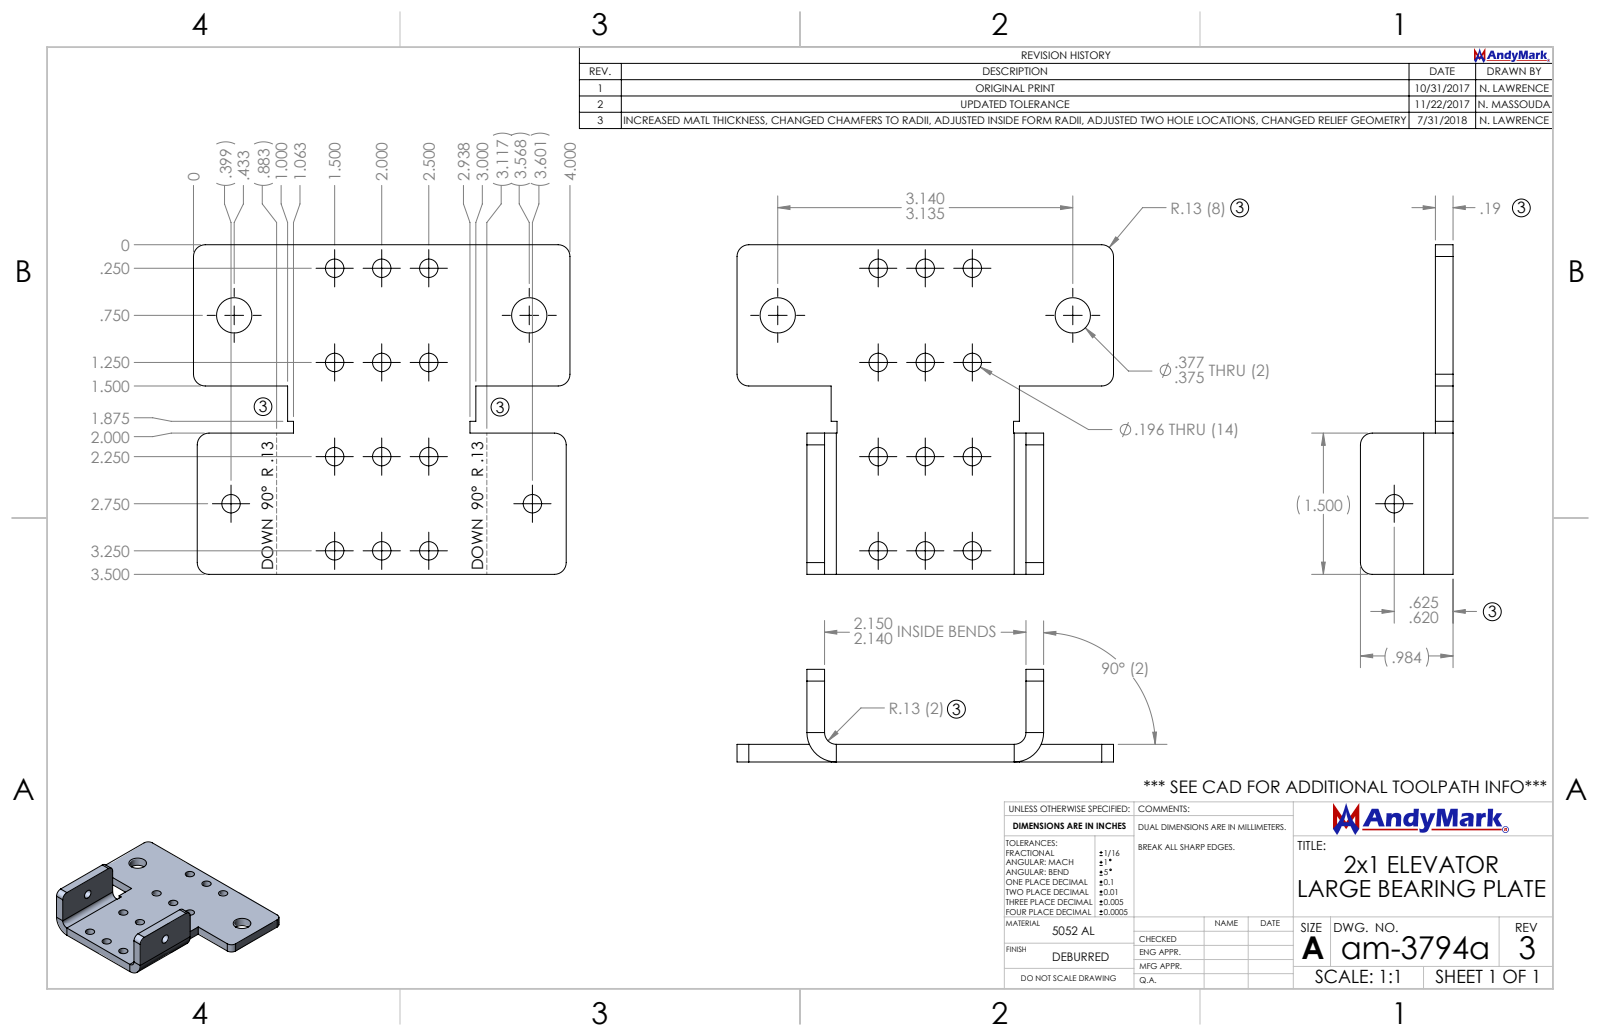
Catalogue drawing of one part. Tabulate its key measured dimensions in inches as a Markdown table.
| quantity | value |
| --- | --- |
| part name | am-3794a 2x1 Elevator Large Bearing Plate R3 |
| STEP written by | SolidWorks 2018 (AUTOMOTIVE_DESIGN) |
| units | inches |
| bodies | 1 solid, 58 faces (30 planar, 28 cylindrical, 0 other) |
| overall size | 4 × 3.5 × 0.984 |
| volume | 2.286 in³ |
| surface area | 29.95 in² |
| round holes (diameter × count) | 0.196 × 13, 0.375 × 2 |
| partial cylindrical surfaces (radius × count) | 0.125 × 8, 0.313 × 2 |
| main face-to-face distances | 0.187, 2.328, 2.515, 2.14, 2, 3.5, 1.5, 0.743, 0.93, 3.07 |
| hole center spacings | 1, 1.118, 0.5, 2.061, 1.414, 2, 1.179, 1.645 |
